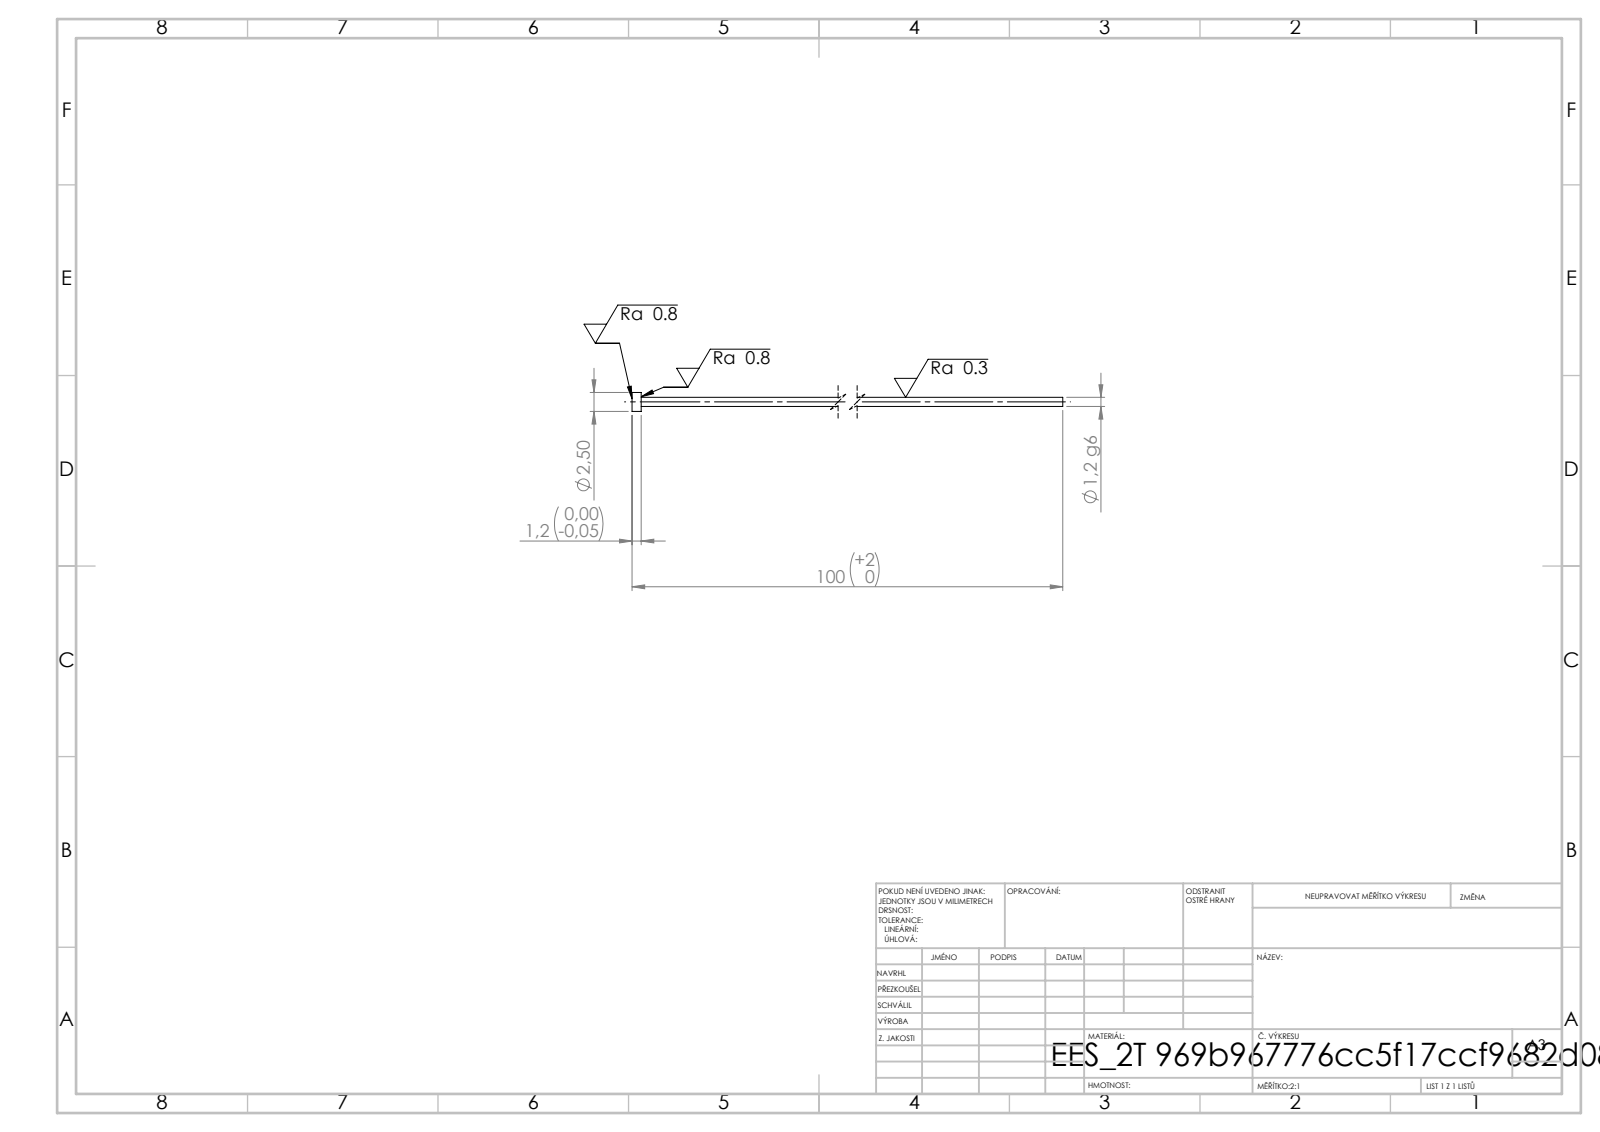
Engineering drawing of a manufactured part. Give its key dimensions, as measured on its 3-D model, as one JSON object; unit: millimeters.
{"step_written_by": "SolidWorks 2019 (CONFIG_CONTROL_DESIGN)", "units": "millimeters", "bodies": {"solids": 1, "faces": 7, "planar": 3, "cylindrical": 4, "other": 0}, "overall_size": [100, 2.5, 2.5], "volume_mm3": 118, "surface_area_mm2": 392, "round_bosses_or_shafts": [[2.5, 1], [1.2, 1]], "face_to_face_distances": [1.2, 100, 98.8]}
